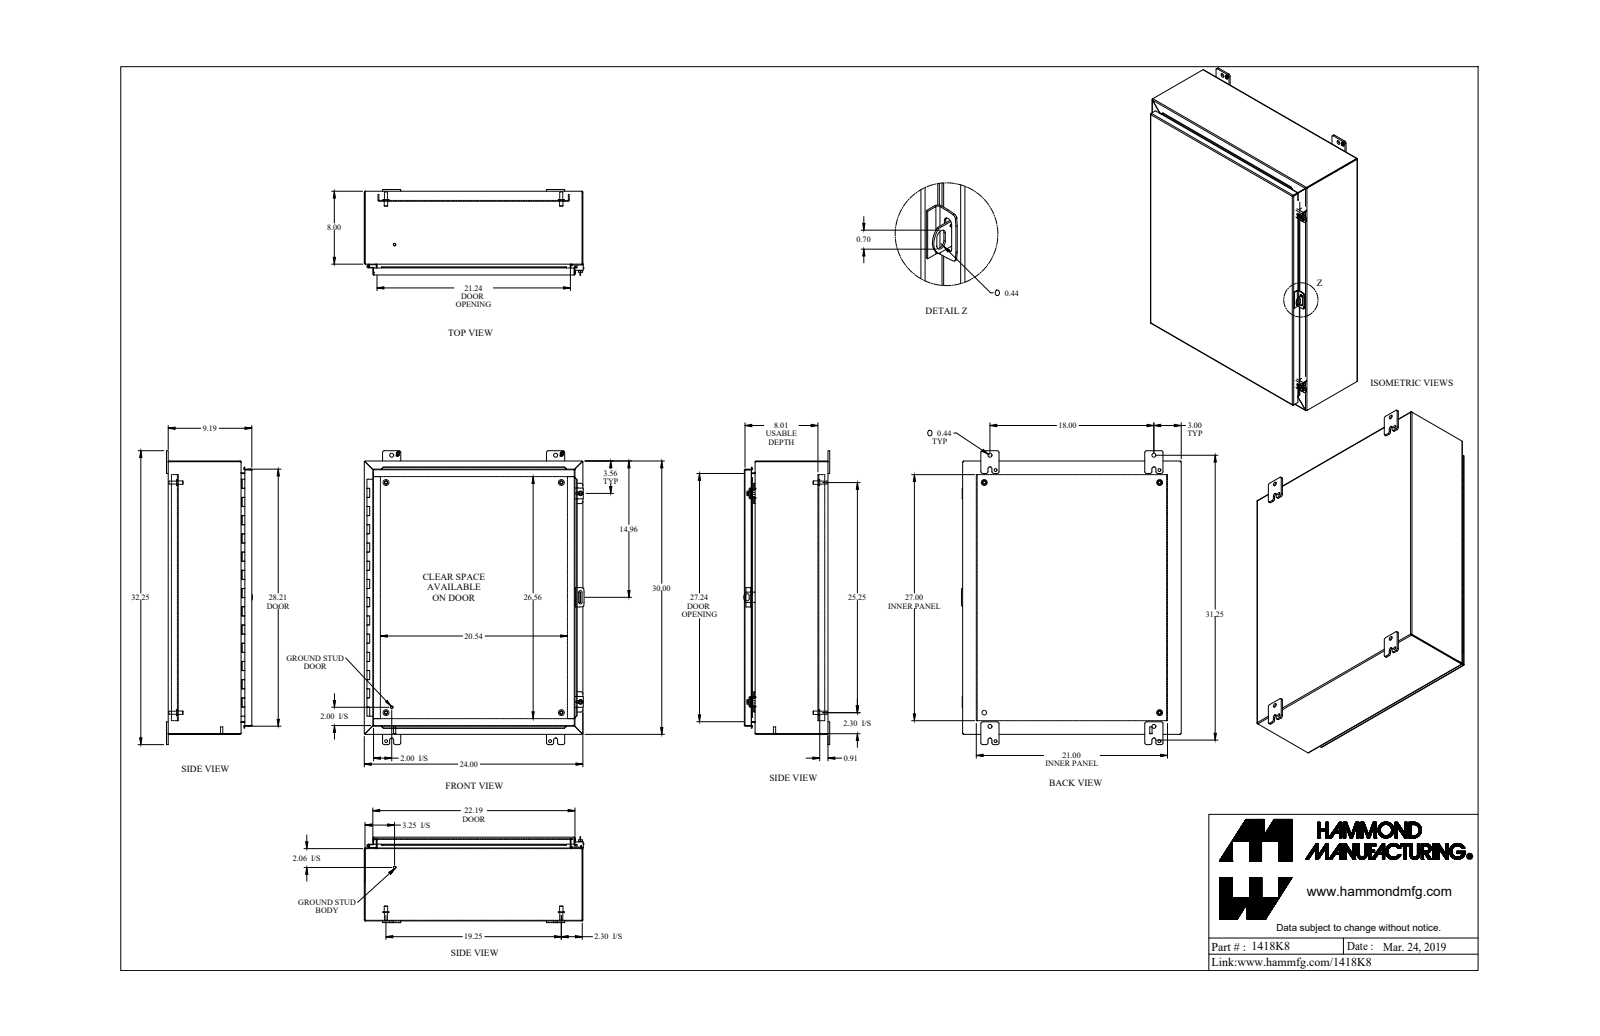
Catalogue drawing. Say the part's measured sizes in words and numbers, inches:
The part is named "1418K8_Default". Its 3-D file was written by "SolidWorks 2019 (CONFIG_CONTROL_DESIGN)". It is 38 solids with 1209 faces: 739 planar, 402 cylindrical and 68 other. Overall it measures 32.25 by 24.125 by 9.437 inches. Its volume is 263.5 cubic inches and its surface area 6 817 square inches. Round holes: 4 of diameter 0.313, 4 of diameter 0.437, 4 of diameter 0.5, 2 of diameter 0.213, 2 of diameter 0.265, 2 of diameter 0.307, 2 of diameter 0.375, 2 of diameter 0.445, 1 of diameter 0.125, 1 of diameter 0.187. Round bosses or shafts: 4 of diameter 0.65, 4 of diameter 0.375, 4 of diameter 0.33, 2 of diameter 1, 2 of diameter 0.5, 2 of diameter 0.39, 2 of diameter 0.281, 2 of diameter 0.25. Partial cylindrical surfaces (rounded edges, fillets, slot ends): 26 of radius 0.188, 24 of radius 0.036, 24 of radius 0.108, 13 of radius 0.048, 13 of radius 0.143, 8 of radius 0.045, 8 of radius 0.218, 8 of radius 0.25. The main face-to-face distances are 0.072, 9.113, 9.041, 9.185, 0.937, 0.095, 1.009, 8.081, 8.009, 1.032. The hole center spacings are 1.735, 18, 25.25, 29.75, 31.751, 34.772, 3.064, 19.25.
